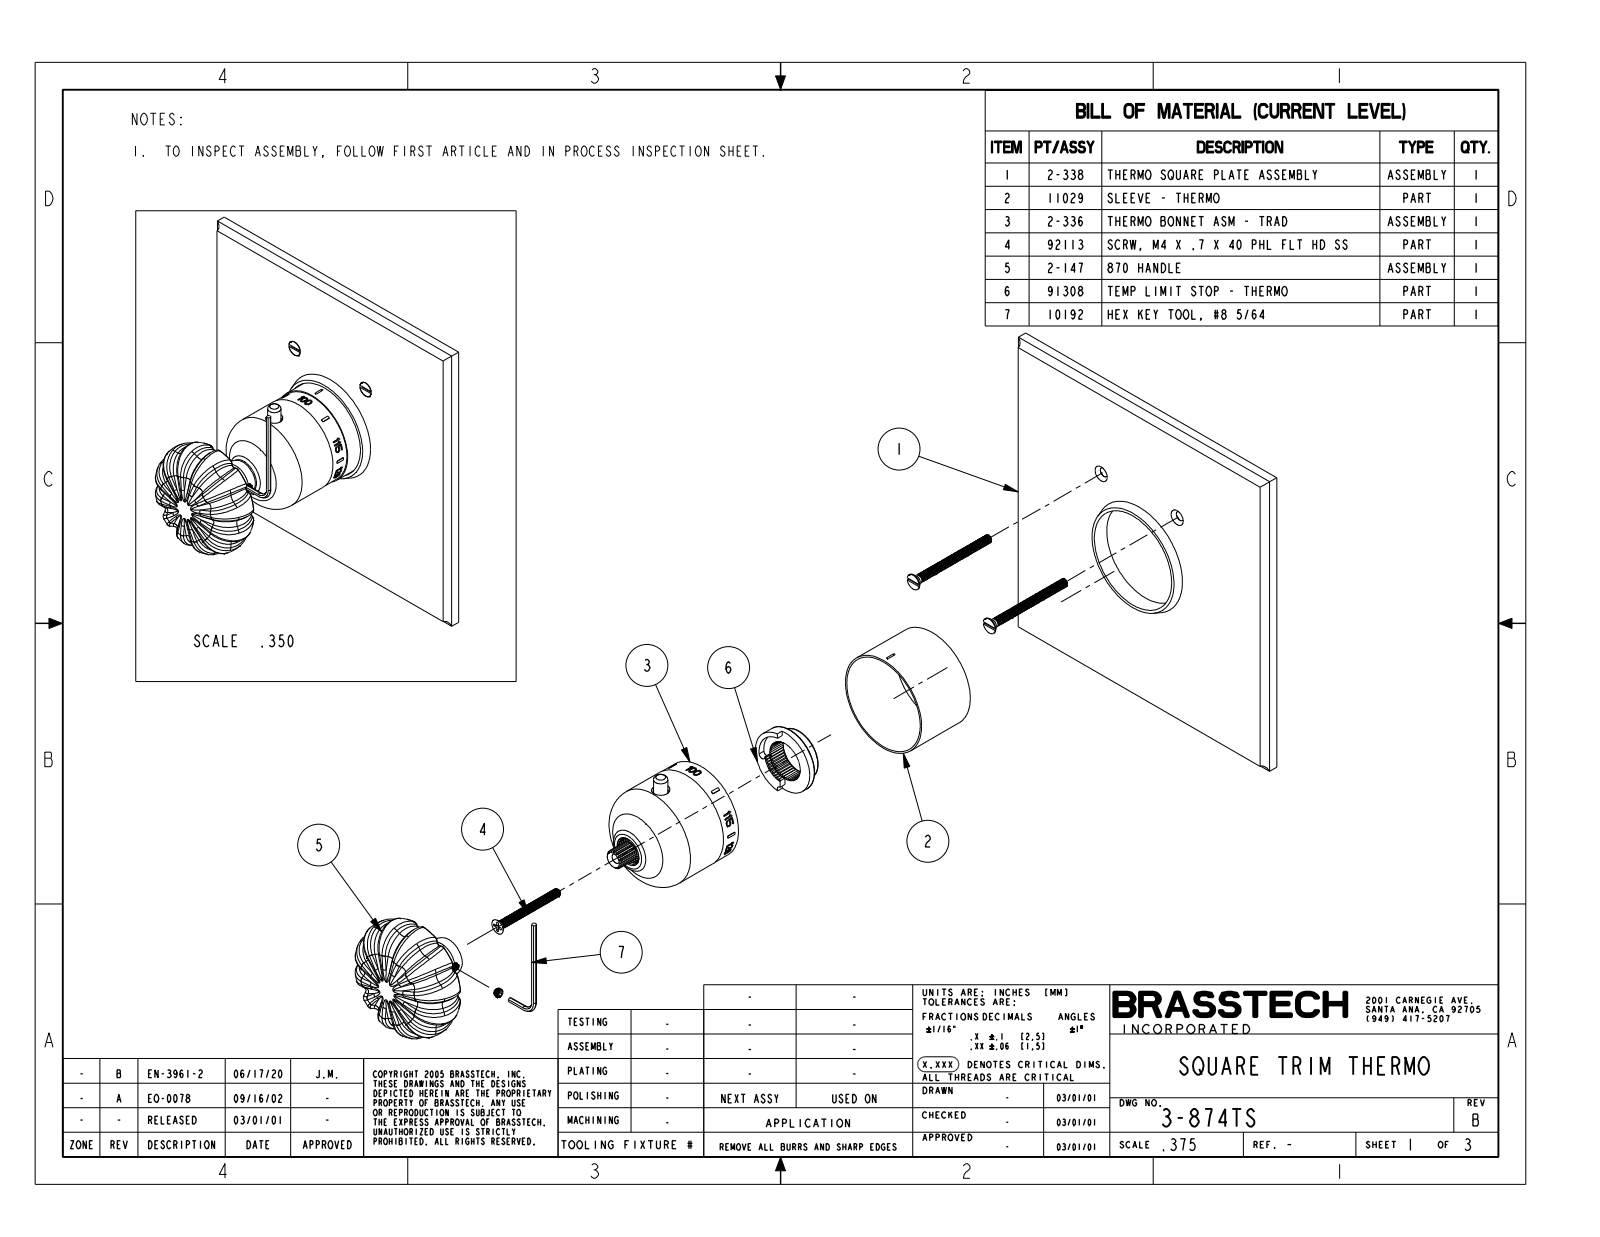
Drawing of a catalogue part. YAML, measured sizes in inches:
part_name: "3-874TS"
step_written_by: "CREO PARAMETRIC BY PTC INC, 2018400 (CONFIG_CONTROL_DESIGN)"
units: inches
bodies: {solids: 1, faces: 687, planar: 332, cylindrical: 35, other: 320}
overall_size: [6.5, 6.5, 4.356]
volume: 22.5
surface_area: 118
round_bosses_or_shafts:
  - {diameter: 1.97, count: 1}
  - {diameter: 1.94, count: 1}
  - {diameter: 1.929, count: 1}
  - {diameter: 0.37, count: 1}
  - {diameter: 0.26, count: 1}
  - {diameter: 0.067, count: 1}
partial_cylinders:
  - {radius: 0.125, count: 4}
  - {radius: 0.969, count: 1}
face_to_face_distances: [0.313, 3.486, 3.173, 6.5, 2.705, 2.392, 0.781, 2.736, 2.423, 0.031]
